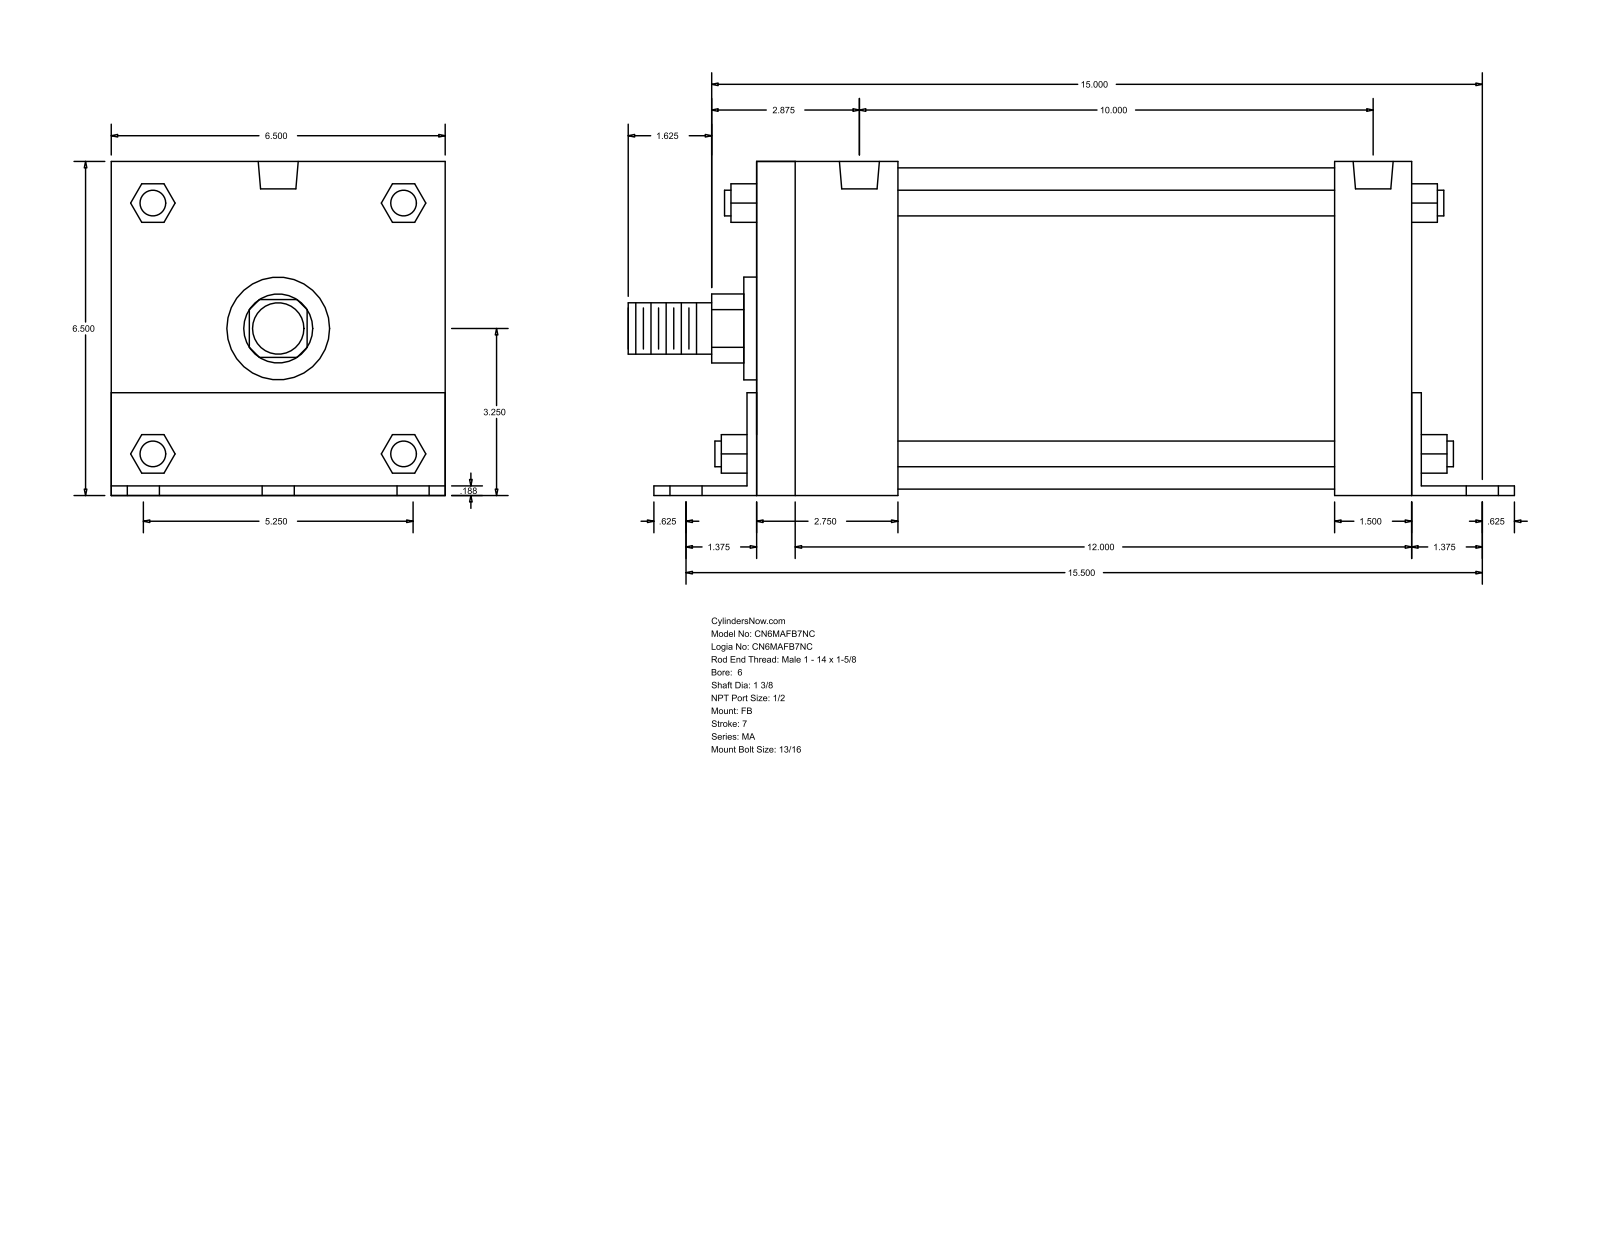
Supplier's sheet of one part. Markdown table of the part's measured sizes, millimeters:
| quantity | value |
| --- | --- |
| part name | MA_FB__0600_1.375 |
| STEP written by | GSSL Pune (CONFIG_CONTROL_DESIGN) |
| units | millimeters |
| bodies | 0 solids, 140 faces (105 planar, 35 cylindrical, 0 other) |
| overall size | 434.98 × 165.15 × 165.1 |
| round holes (diameter × count) | 20.64 × 6, 17.46 × 4, 19.77 × 2 |
| round bosses / shafts (diameter × count) | 12.7 × 4, 158.75 × 1, 50.8 × 1, 34.92 × 1, 25.4 × 1 |
| partial cylindrical surfaces (radius × count) | 17.06 × 1, 32.05 × 1 |
| main face-to-face distances | 165.1, 4.76, 320.67, 165.15, 4.71, 160.39, 4.77, 38.1, 42.86, 330.2 |
| hole center spacings | 66.67, 396.17, 390.52, 83.82, 85.78, 108.6, 133.34, 250.82 |
